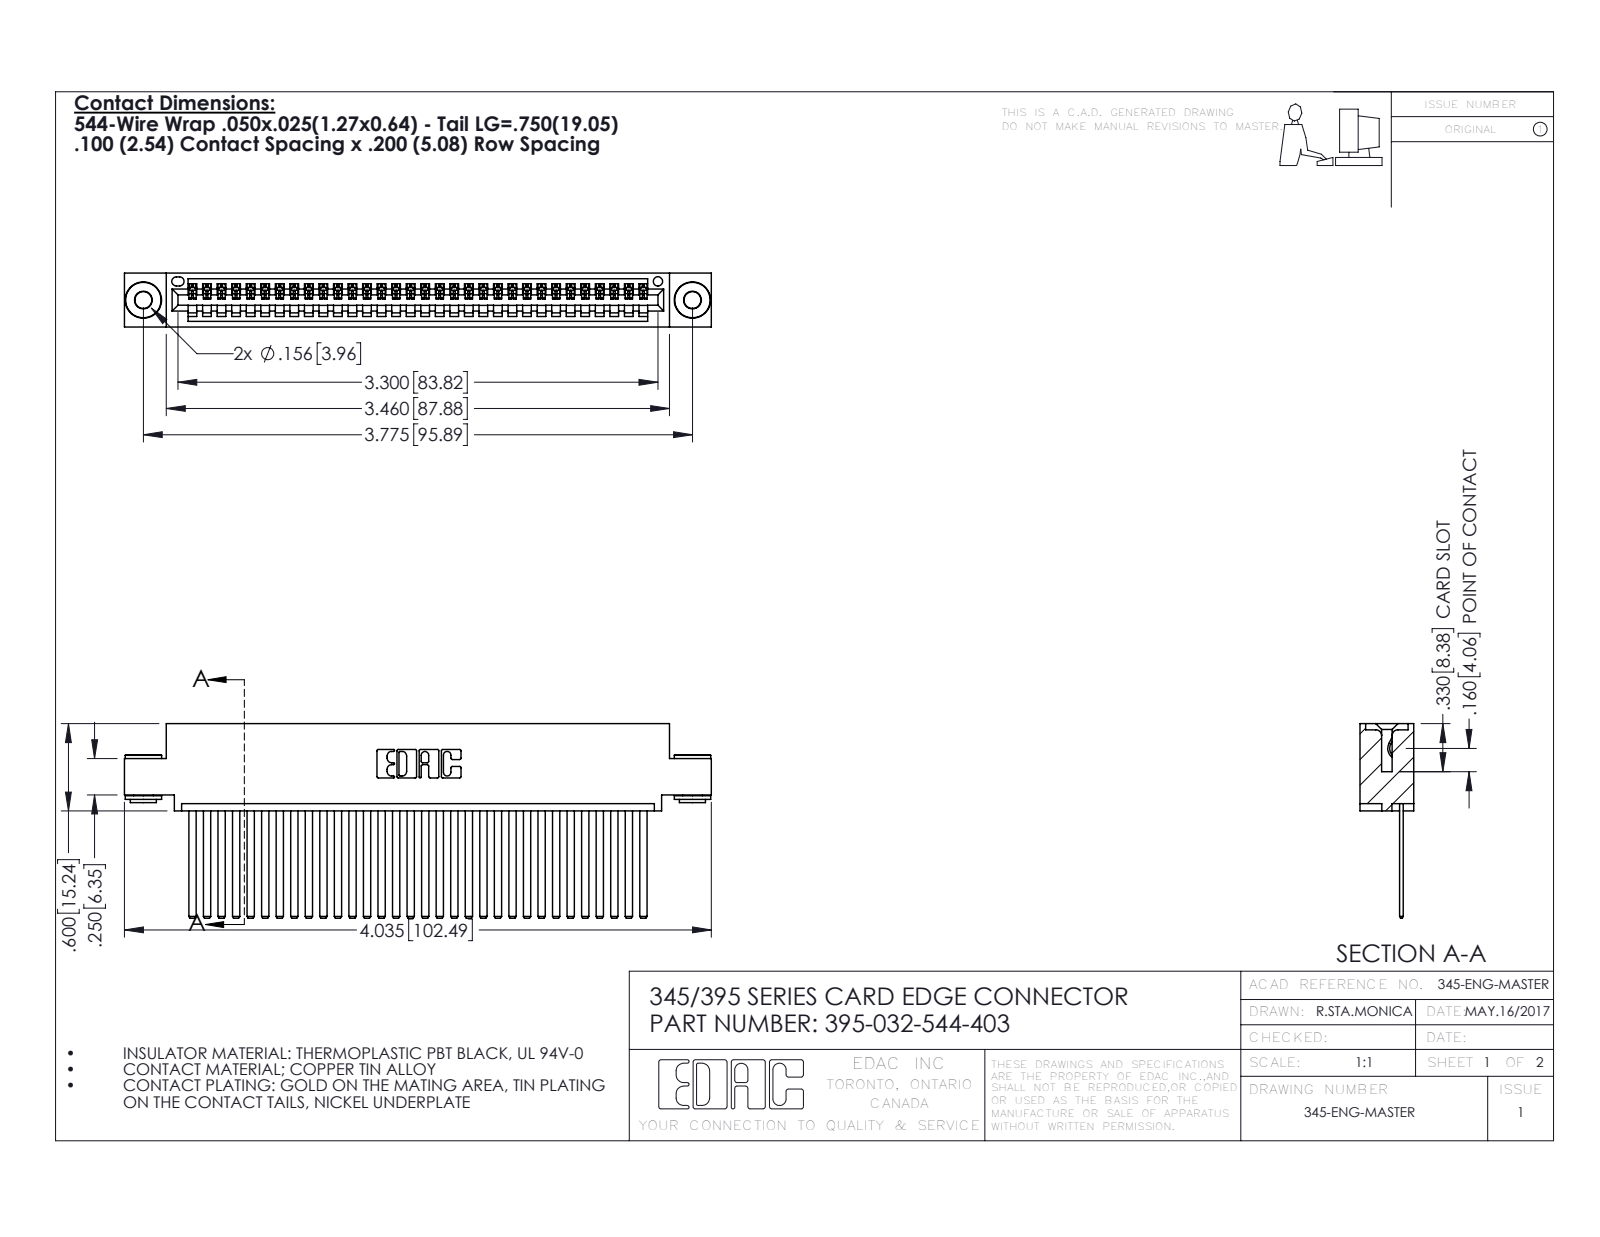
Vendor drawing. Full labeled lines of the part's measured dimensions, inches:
Part name (STEP PRODUCT): 345-250-002_345-250-002-102; 345 Part_0.110 Offset - 0.156 Dia-TH; 395-032-544-403; 345-292-001_345-293-144
STEP written by: SolidWorks 2016 (CONFIG_CONTROL_DESIGN)
Units: inches
Bodies: 35 solids, 1832 faces (1246 planar, 578 cylindrical, 8 other)
Overall size (bounding box): 4.035 × 1.337 × 0.37
Volume: 0.608 in³ · Surface area: 22.51 in²
Round holes (diameter × count): ⌀0.116 ×2, ⌀0.156 ×2, ⌀0.064 ×1
Round bosses / shafts (diameter × count): ⌀0.25 ×2, ⌀0.18 ×2, ⌀0.136 ×2
Partial cylindrical surfaces — rounded edges, fillets, slot ends (radius × count): R0.006 ×64, R0.01 ×22, R0.007 ×6, R0.031 ×6, R0.026 ×3, R0.031 ×2, R0.04 ×2, R0.014 ×1
Main face-to-face distances: 0.072, 0.298, 0.025, 0.098, 0.272, 0.37, 0.2, 0.225, 0.149, 0.072
Hole centre spacings: 0.27, 3.54, 3.775
